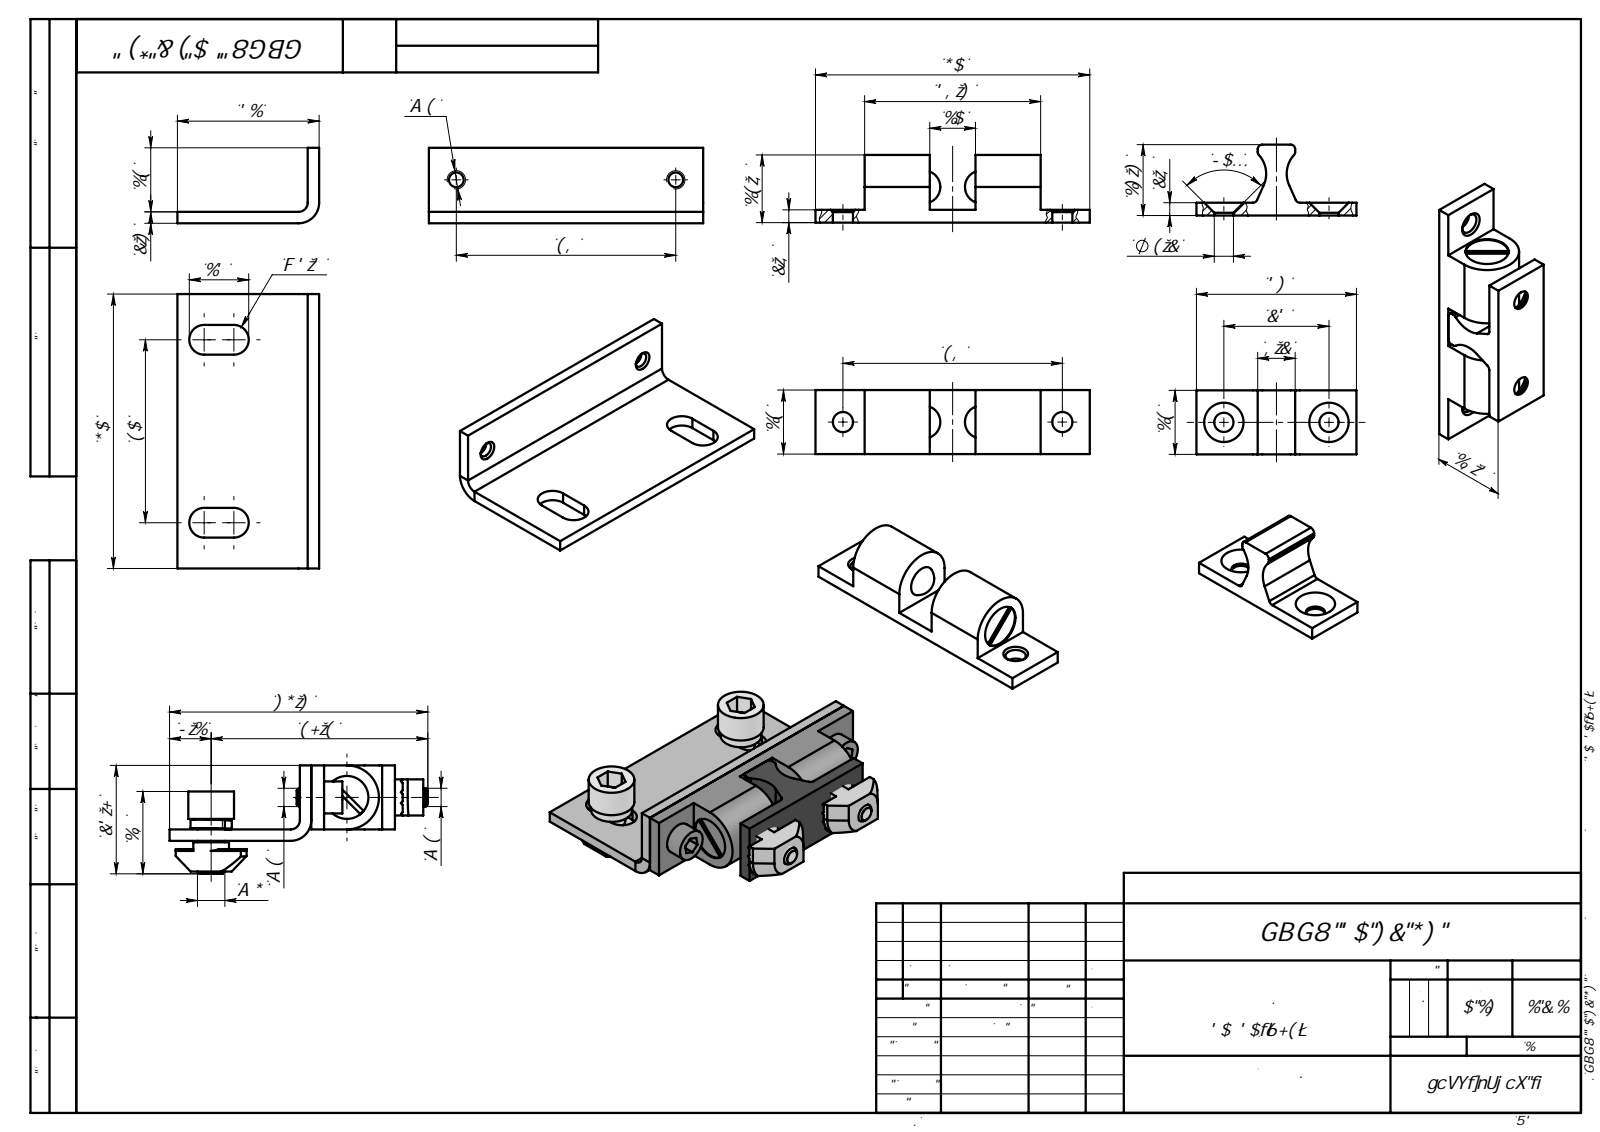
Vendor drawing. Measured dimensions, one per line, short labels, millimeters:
name: SNSD.30.51.45. Т-Гайка М4, паз 8(D50)_00; B62B66SNSD.30.50.85. Винт M6x20(B59)B62B59B5312B74; SNSD.30.51.47. Т-Гайка М6, паз 8(D53); B62B66SNSD.30.50.85. Винт M4x10(B59)B62B59B5312B74 (+4 more)
written by: SolidWorks 2014 (AUTOMOTIVE_DESIGN)
unit: mm
bodies: 15 solids, 413 faces (248 planar, 93 cylindrical, 72 other)
size: 7499.71 × 7499.68 × 408.65
volume: 19 106 mm³; area: 15 244 mm²
holes: 4× ⌀3.2, 2× ⌀4.2, 2× ⌀4.4, 2× ⌀5, 2× ⌀6.25, 1× ⌀9.4
bosses: 4× ⌀4, 2× ⌀10, 2× ⌀9.03, 2× ⌀8, 2× ⌀7, 2× ⌀6
rounds: 8× R4, 8× R6.87, 6× R1, 4× R3.25, 2× R6.1, 1× R2, 1× R4.5, 1× R7
face distances: 2.5, 2.8, 15.5, 14, 16.5, 5.3, 20.8, 18.3, 18, 10.95
hole spacings: 12.5, 35.5, 23, 40, 48
